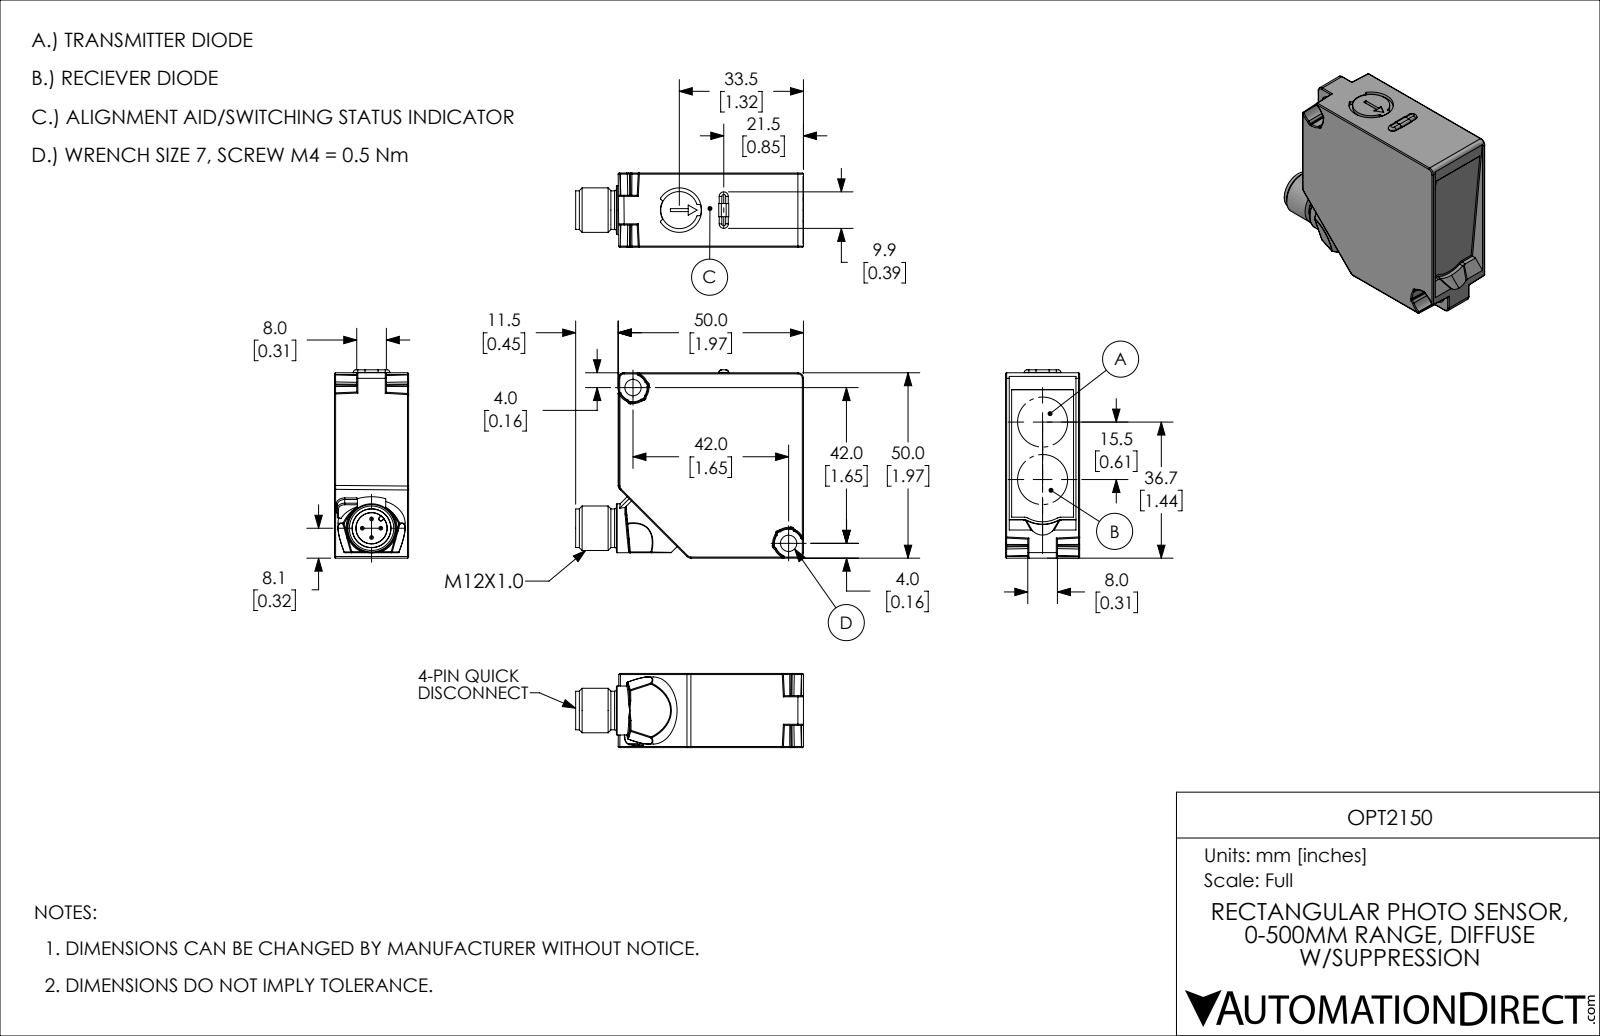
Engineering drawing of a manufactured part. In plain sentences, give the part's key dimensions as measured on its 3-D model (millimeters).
The part is named "OPT2150". Its 3-D file was written by "SolidWorks 2019 (AUTOMOTIVE_DESIGN)". It is 1 solid with 342 faces: 109 planar, 120 cylindrical and 113 other. Overall it measures 61.5 by 50.8 by 20 millimeters. Its volume is 46 150 cubic millimeters and its surface area 10 090 square millimeters. Round holes: 2 of diameter 4.4, 1 of diameter 12, 1 of diameter 18.1. Round bosses or shafts: 4 of diameter 1, 1 of diameter 13.2, 1 of diameter 12, 1 of diameter 10.4, 1 of diameter 10. Partial cylindrical surfaces (rounded edges, fillets, slot ends): 64 of radius 0.3, 8 of radius 0.2, 5 of radius 1.5, 5 of radius 2, 4 of radius 0.7, 2 of radius 1.2, 1 of radius 5.1, 1 of radius 5.9. The main face-to-face distances are 20, 50, 1, 19, 6, 14, 5, 13, 1.5, 48.5. The hole center spacings are 59.4.
